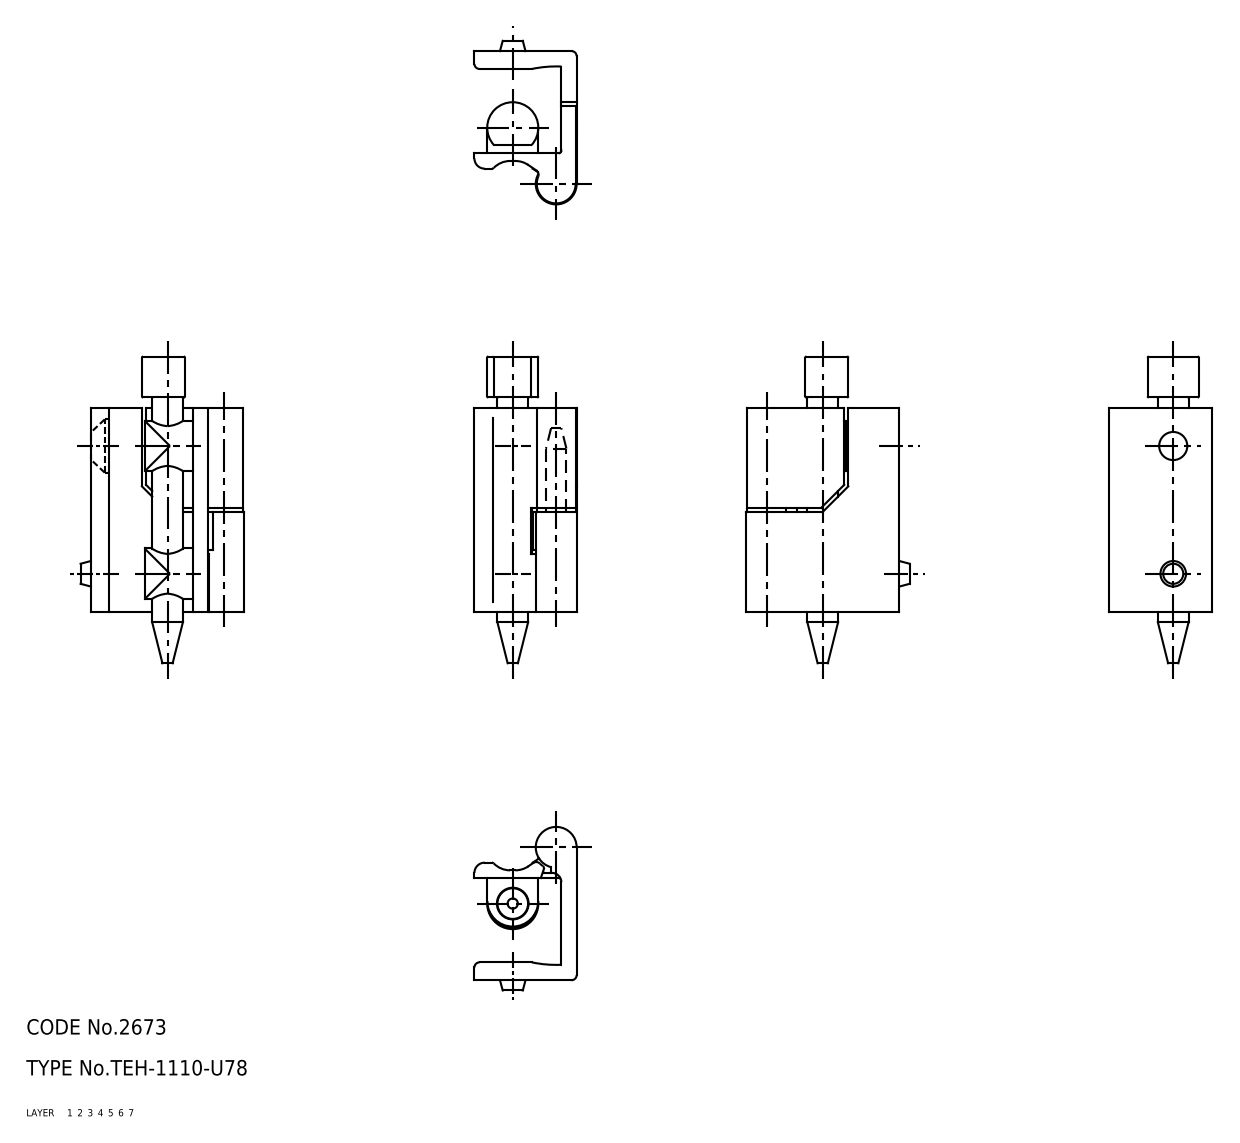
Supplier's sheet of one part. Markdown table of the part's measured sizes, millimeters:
| quantity | value |
| --- | --- |
| part name | washer; shaft; pin; hinge pieces_B (+2 more) |
| STEP written by | CADfix (AUTOMOTIVE_DESIGN) |
| units | millimeters |
| bodies | 5 solids, 105 faces (0 planar, 0 cylindrical, 105 other) |
| overall size | 60 × 32 × 20 |
| volume | 10 822 mm³ |
| surface area | 8 956 mm² |
